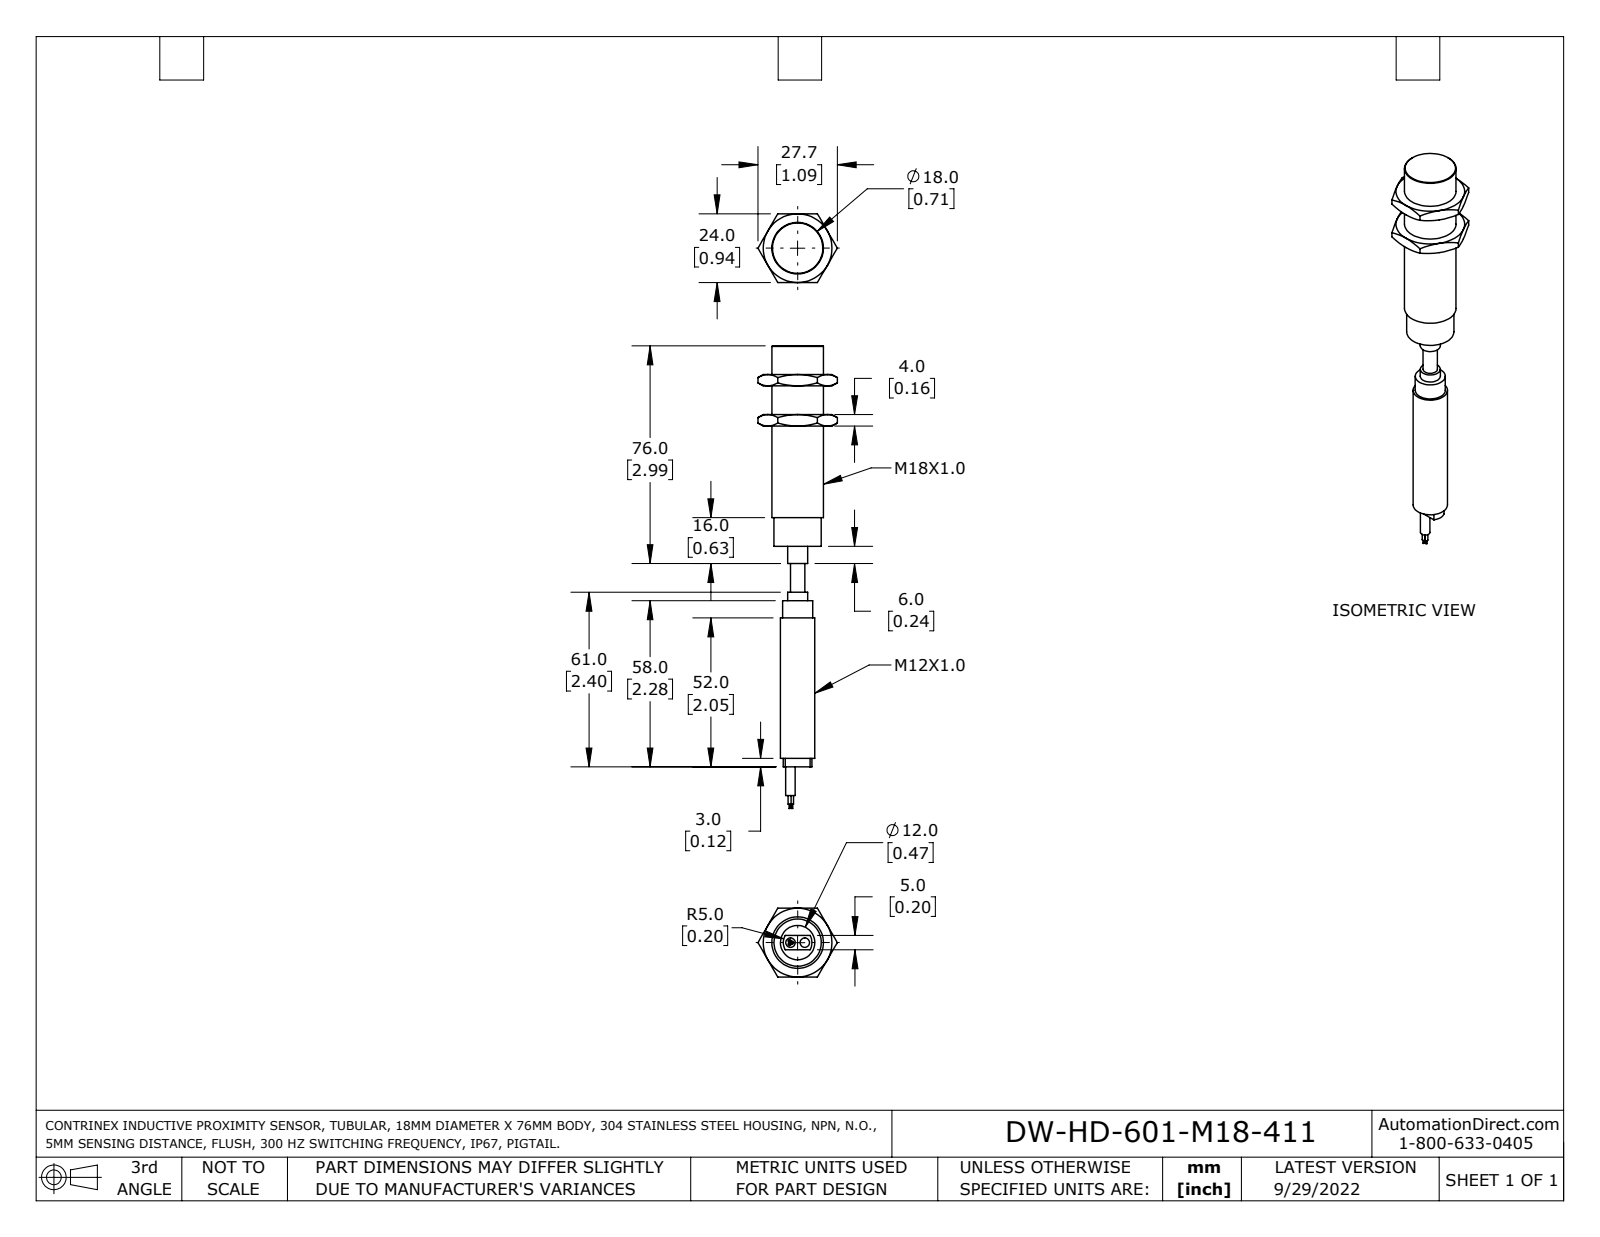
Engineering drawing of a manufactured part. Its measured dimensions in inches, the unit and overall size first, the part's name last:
Units: inches
Overall size (bounding box): 6.358 × 1.091 × 0.945
Round holes (diameter × count): ⌀0.13 ×1
Round bosses / shafts (diameter × count): ⌀0.039 ×3, ⌀0.016 ×3, ⌀0.709 ×1, ⌀0.65 ×1, ⌀0.472 ×1, ⌀0.413 ×1, ⌀0.276 ×1, ⌀0.197 ×1
Partial cylindrical surfaces — rounded edges, fillets, slot ends (radius × count): R0.197 ×1
Main face-to-face distances: 0.551, 0.394, 0.157, 0.945, 2.362, 1.811, 1.102, 0.709, 0.944, 2.756
Volume: 1.594 in³ · Surface area: 12.94 in²
Bodies: 1 solid, 79 faces (35 planar, 19 cylindrical, 25 other)
Part name (STEP PRODUCT): DW-HD-601-M18-411
STEP written by: SolidWorks 2021 (AUTOMOTIVE_DESIGN)
